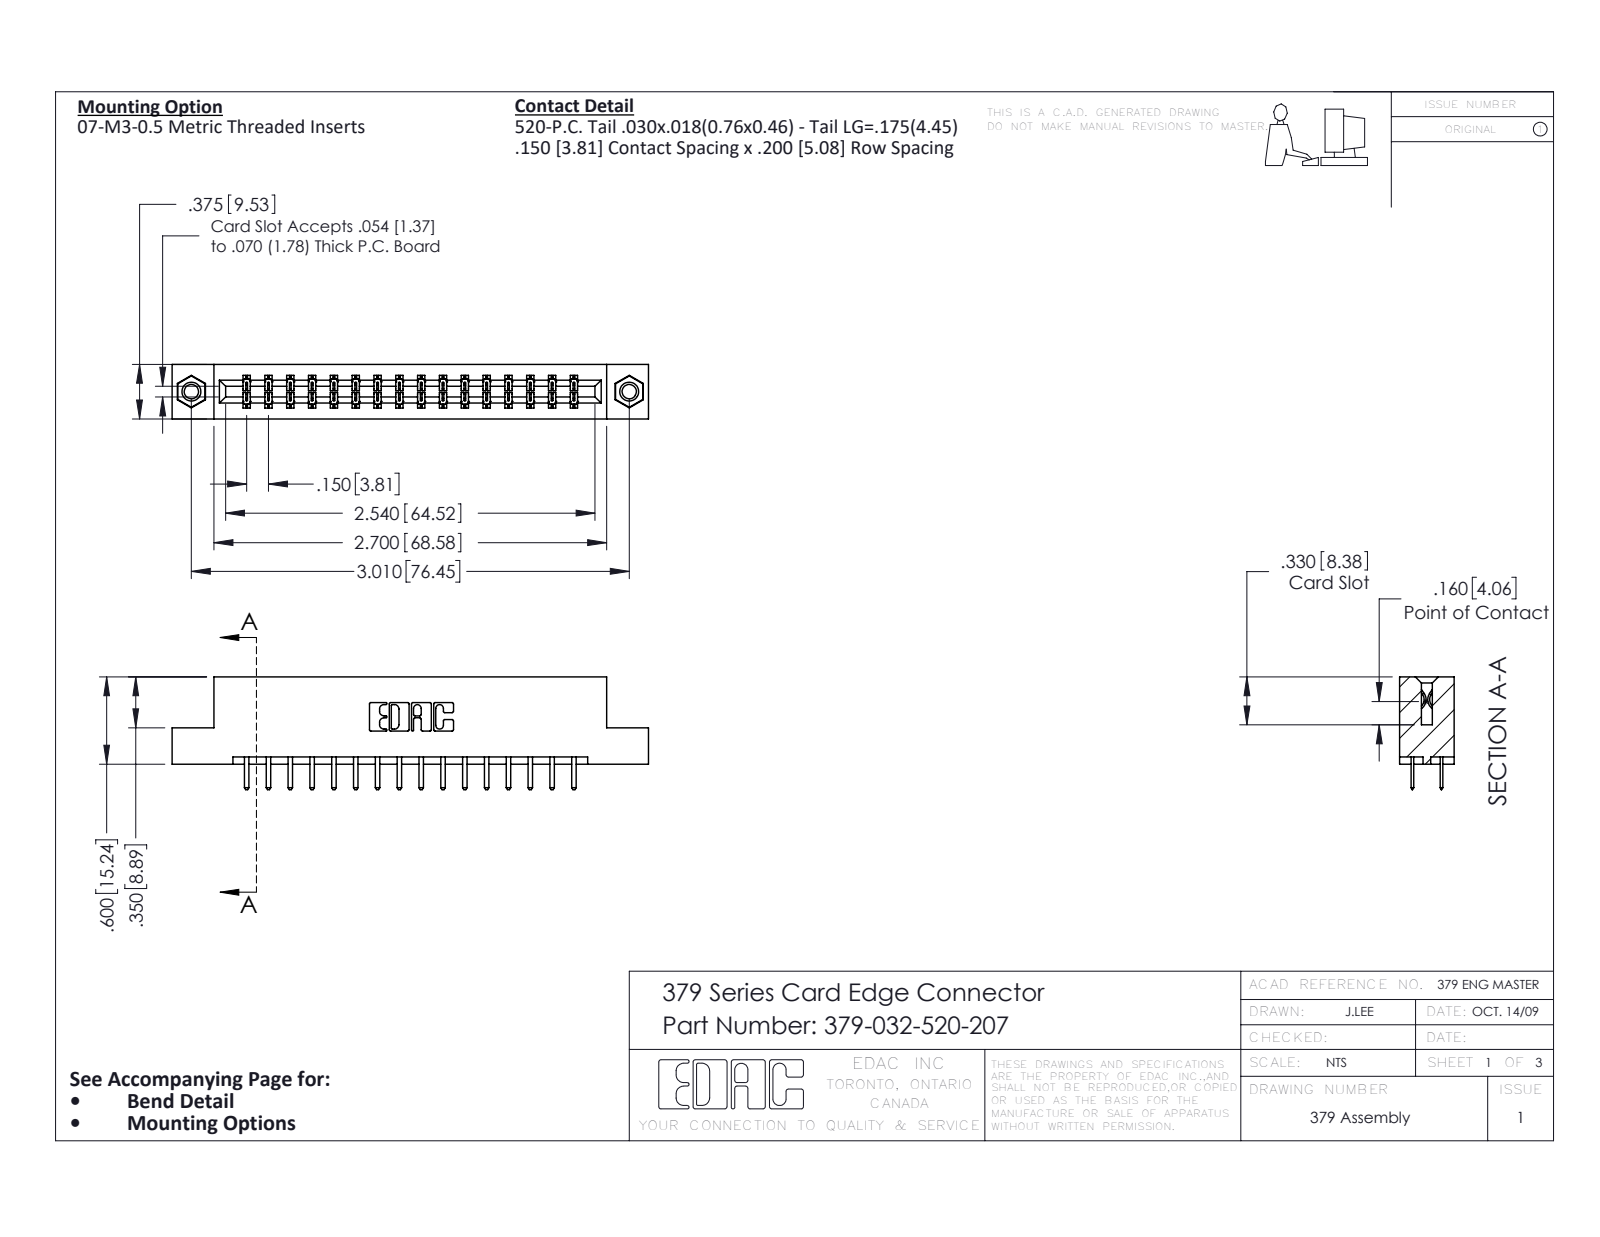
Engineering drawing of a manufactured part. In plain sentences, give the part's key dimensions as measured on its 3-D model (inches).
The part is named "345-250-001_345-250-005-103; 345-292-001_345-293-120; 379-032-520-207; 379 Part_Flush - .156 Dia - TI". Its 3-D file was written by "SolidWorks 2020 (CONFIG_CONTROL_DESIGN)". It is 35 solids with 1966 faces: 1318 planar, 632 cylindrical and 16 other. Overall it measures 3.275 by 0.775 by 0.375 inches. Its volume is 0.519 cubic inches and its surface area 14.43 square inches. Round holes: 2 of diameter 0.098, 2 of diameter 0.125, 2 of diameter 0.156. Round bosses or shafts: 2 of diameter 0.155. Partial cylindrical surfaces (rounded edges, fillets, slot ends): 63 of radius 0.006, 36 of radius 0.01, 22 of radius 0.01, 6 of radius 0.007, 6 of radius 0.031, 3 of radius 0.026, 2 of radius 0.014, 2 of radius 0.022. The main face-to-face distances are 0.3, 0.375, 0.2, 0.075, 0.1, 0.15, 0.05, 0.6, 0.225, 0.55. The hole center spacings are 3.01.
